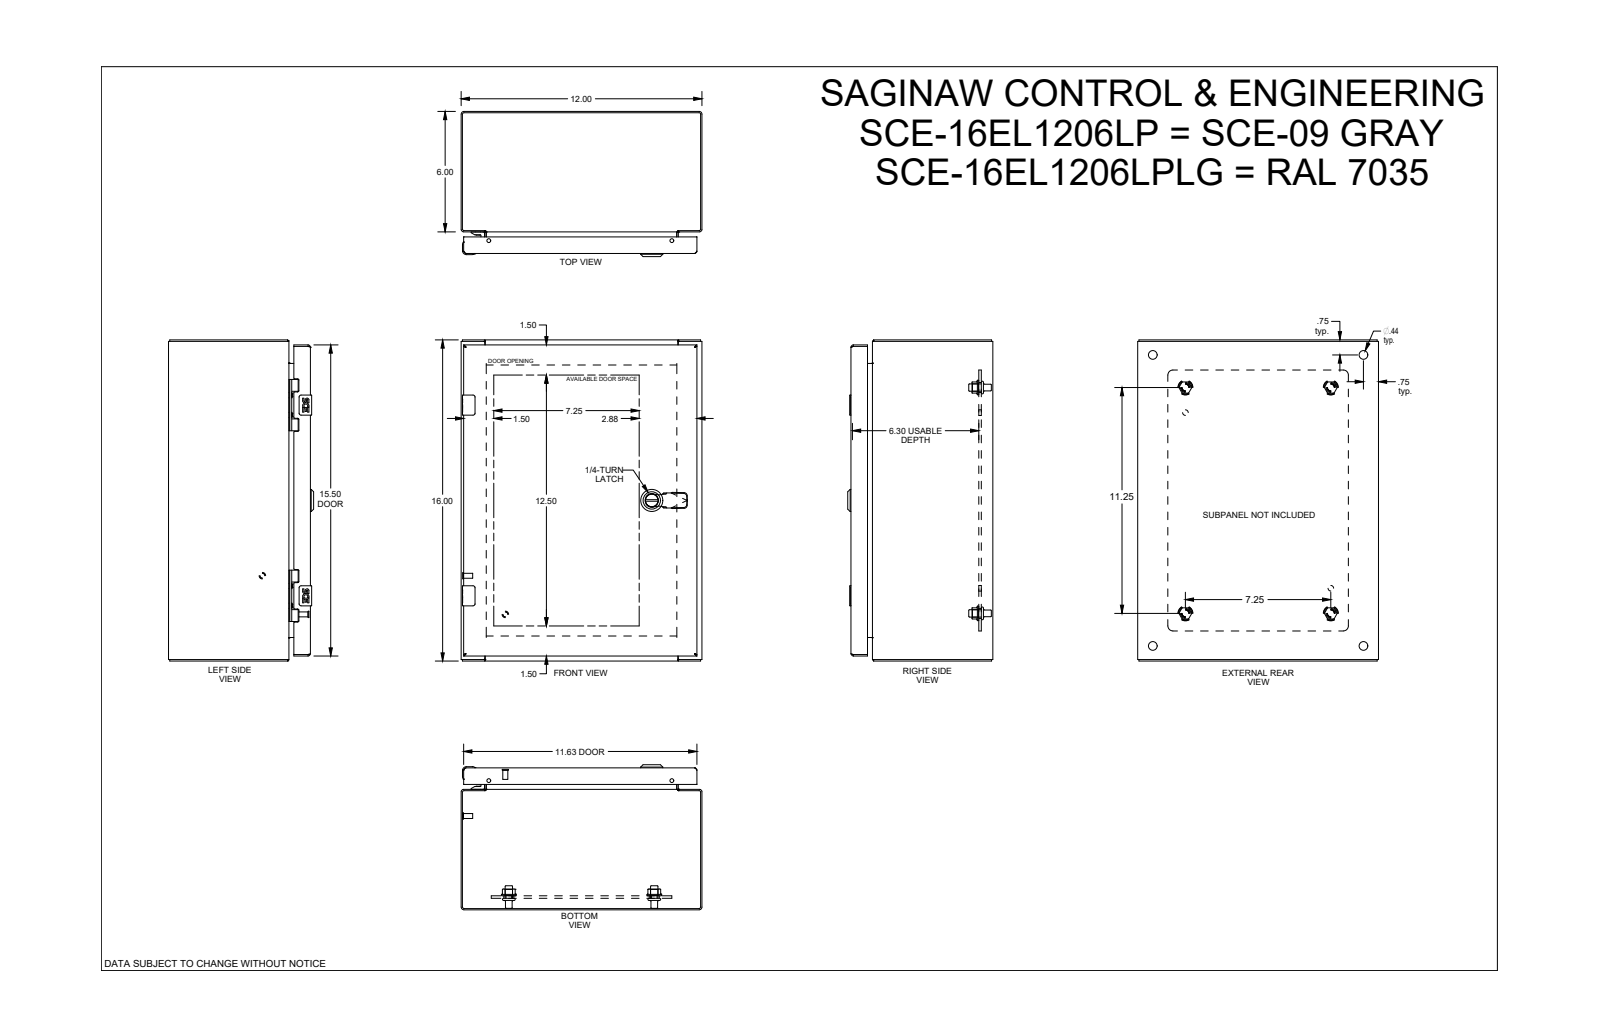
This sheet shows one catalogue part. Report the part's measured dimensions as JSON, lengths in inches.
{"part_name": "SCE-16EL1206LP", "step_written_by": "SolidWorks 2019 (AUTOMOTIVE_DESIGN)", "units": "inches", "bodies": {"solids": 39, "faces": 1793, "planar": 858, "cylindrical": 559, "other": 376}, "overall_size": [16, 12, 7.23], "volume_in3": 84.85, "surface_area_in2": 2070, "round_holes": [[0.172, 4], [0.205, 4], [0.244, 4], [0.266, 4], [0.367, 4], [0.375, 4], [0.437, 4], [0.5, 4], [0.04, 2], [0.156, 2], [0.188, 2], [0.218, 2]], "round_bosses_or_shafts": [[0.17, 6], [0.366, 4], [0.332, 4], [0.25, 4], [0.24, 4], [0.196, 3], [0.248, 2], [1.102, 1]], "partial_cylinders_radius": [[0.012, 30], [0.01, 28], [0.015, 24], [0.06, 13], [0.02, 12], [0.025, 12], [0.1, 12], [0.031, 10]], "face_to_face_distances": [0.075, 0.06, 0.075, 11.925, 7.073, 6.998, 7.013, 6.938, 15.925, 0.125], "hole_center_spacings": [9.5, 0.985, 0.02, 0.493, 0.494, 2.298, 2.993, 9.022]}
